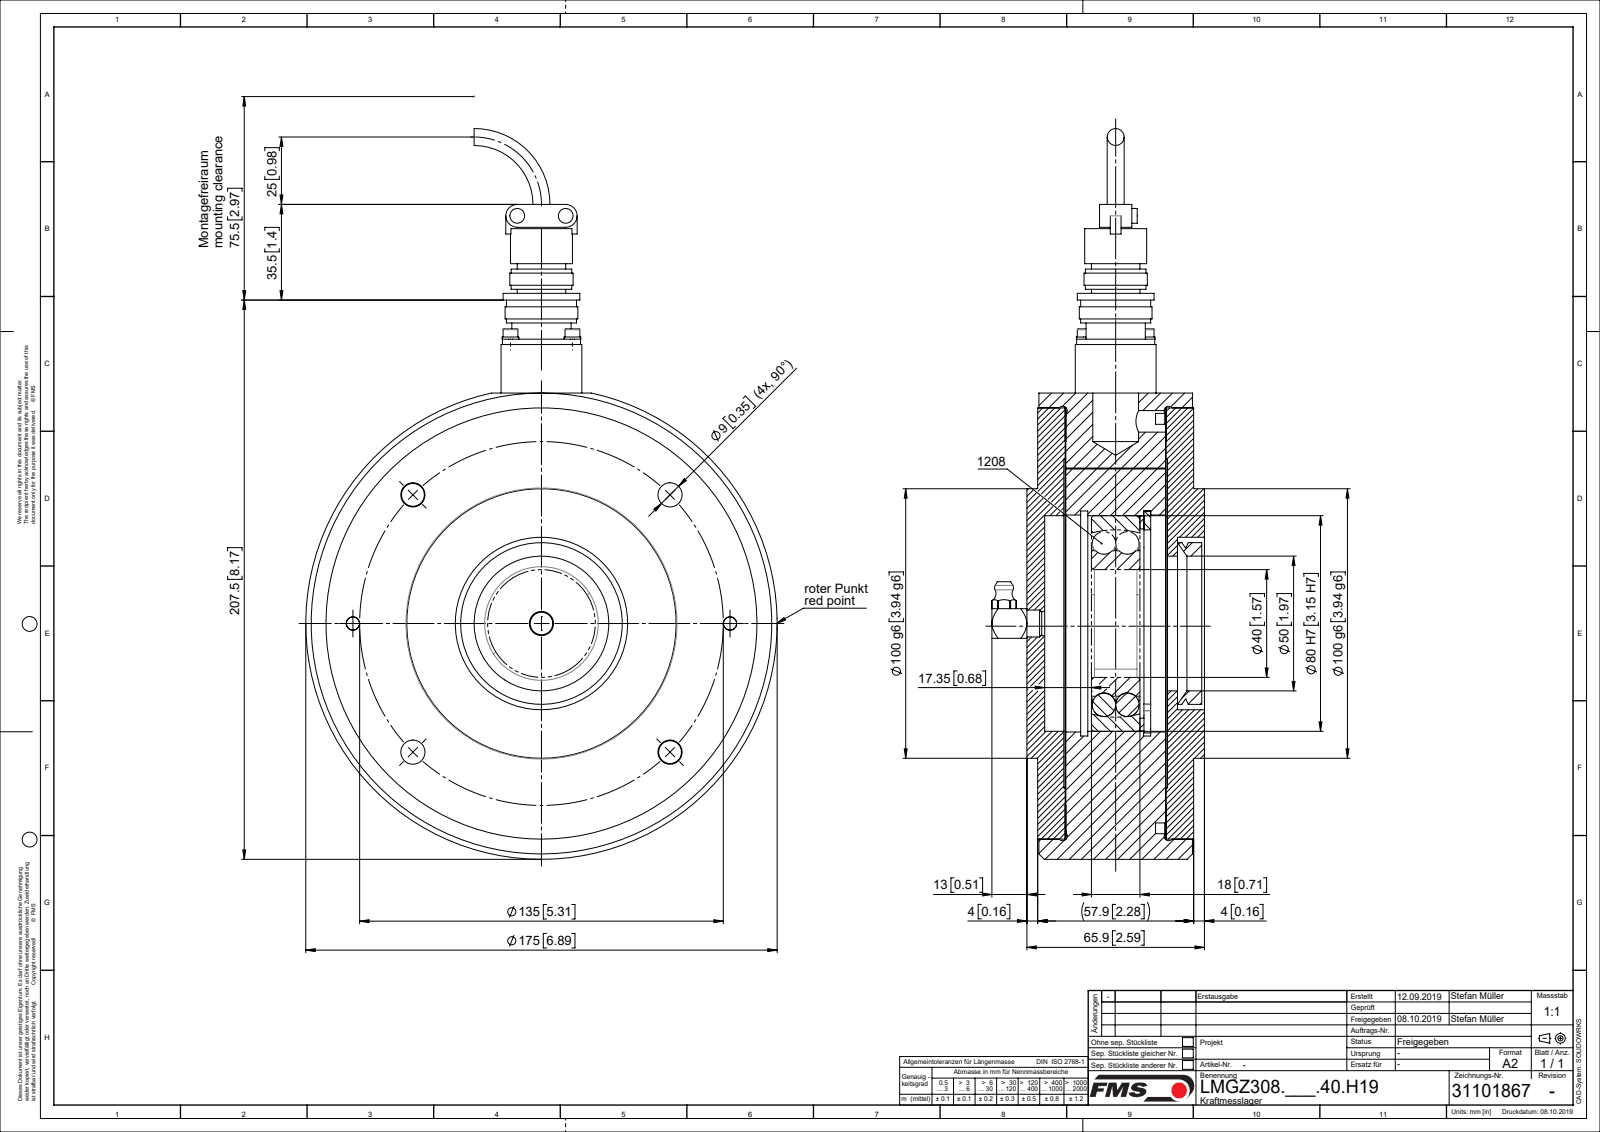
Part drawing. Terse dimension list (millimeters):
name: ZEICHNUNG6; L50049; L4857104; ~TEIL1 (+8 more)
written by: Mechanical Desktop 2009 (CONFIG_CONTROL_DESIGN)
unit: mm
bodies: 23 solids, 419 faces (114 planar, 241 cylindrical, 64 other)
size: 271.15 × 175 × 80.4
volume: 1 270 000 mm³; area: 275 543 mm²
holes: 5× ⌀9, 4× ⌀2.6, 4× ⌀3.2, 4× ⌀3.4, 2× ⌀5.15, 2× ⌀6.6, 2× ⌀8.5, 2× ⌀11, 1× ⌀23, 1× ⌀40, 1× ⌀48, 1× ⌀50
bosses: 6× ⌀5.5, 4× ⌀6.2, 4× ⌀3, 4× ⌀2.5, 3× ⌀10, 2× ⌀6, 1× ⌀175, 1× ⌀160
rounds: 2× R4.25, 2× R7.5
face distances: 37.25, 10.2, 10.45, 47.45, 47.7, 37, 37.5, 0.5, 38, 9.7
hole spacings: 16.26, 23, 52.67, 67.5, 95.46, 127.04, 32.53, 70
